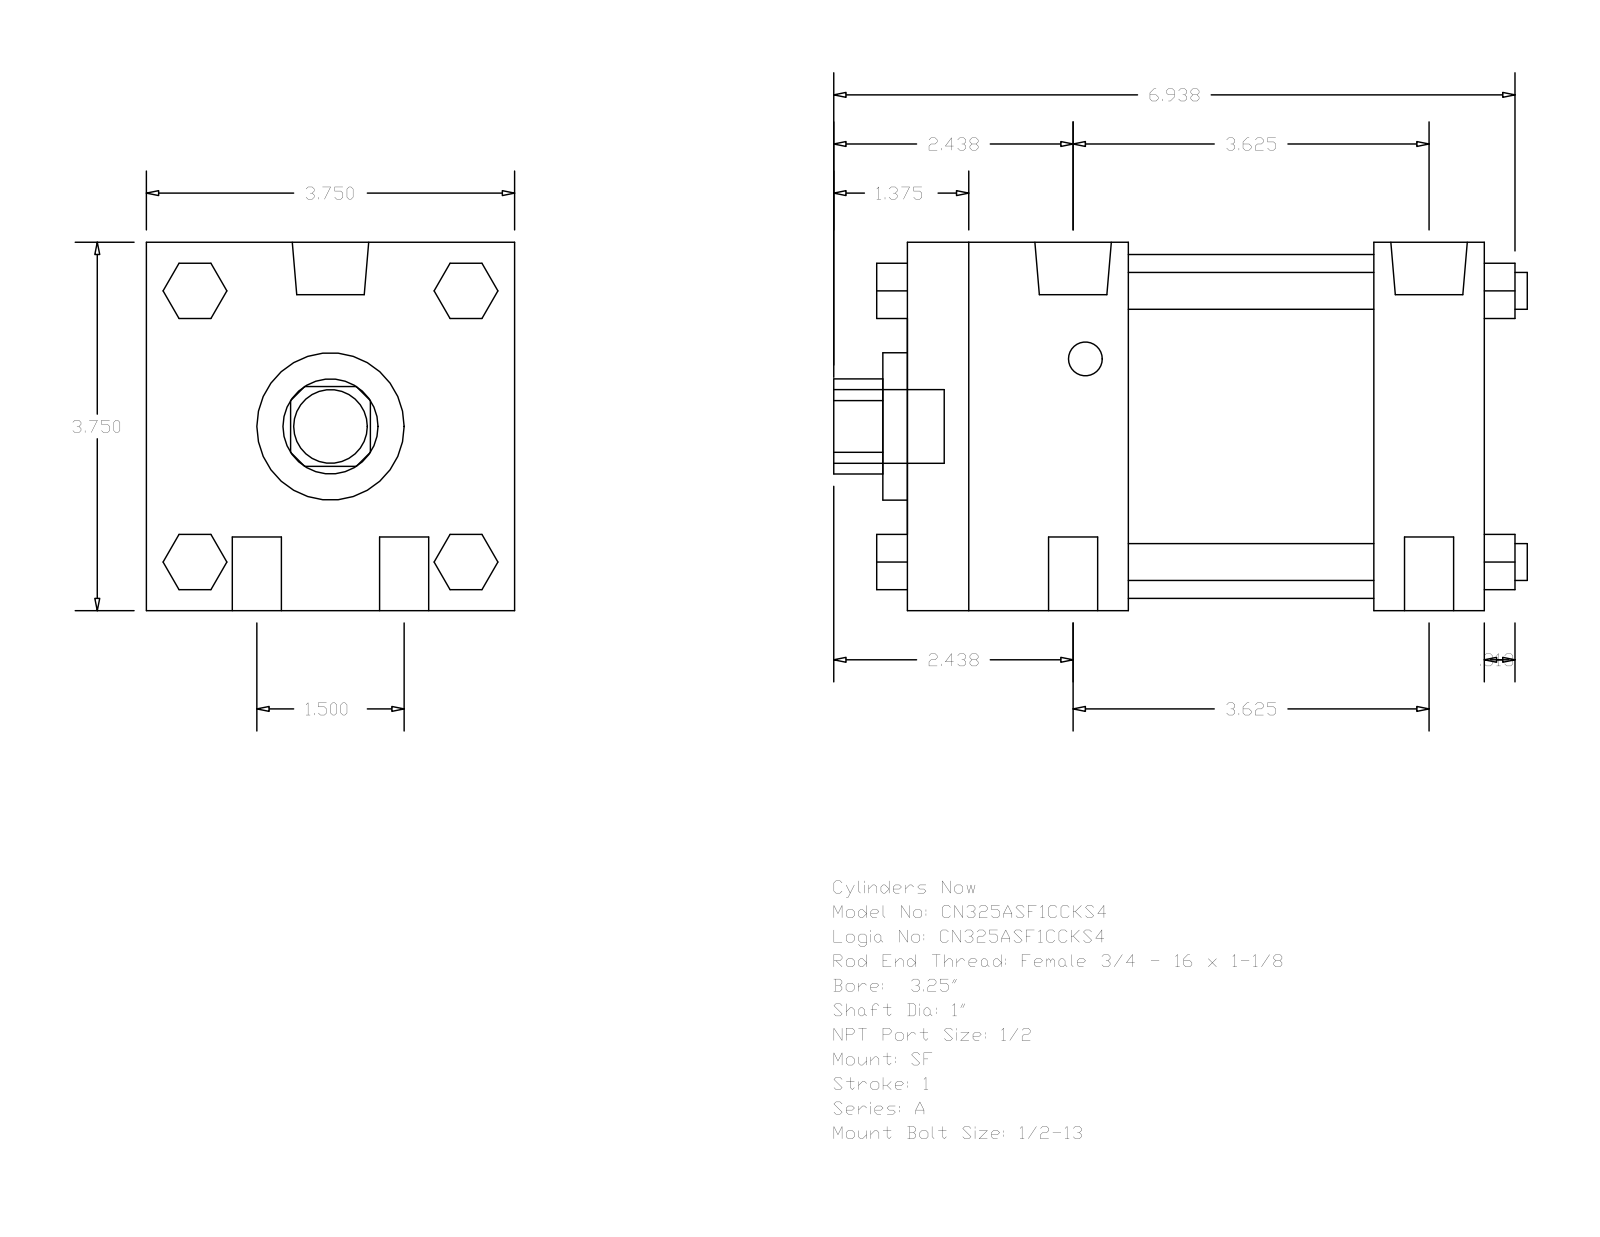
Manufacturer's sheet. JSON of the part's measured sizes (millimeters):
{"part_name": "A_SF__0325_1", "step_written_by": "GSSL Pune (CONFIG_CONTROL_DESIGN)", "units": "millimeters", "bodies": {"solids": 0, "faces": 124, "planar": 94, "cylindrical": 30, "other": 0}, "overall_size": [179.39, 95.25, 95.25], "round_holes": [[25.4, 1], [38.1, 1], [88.9, 1]], "round_bosses_or_shafts": [[12.7, 4], [9.53, 4], [19.77, 2], [8.73, 2], [19.05, 1]], "partial_cylinders_radius": [[12.29, 1]], "face_to_face_distances": [95.24, 149.23, 63.5, 120.65, 28.58, 57.15, 92.08, 14.28, 35.05, 60.71]}
